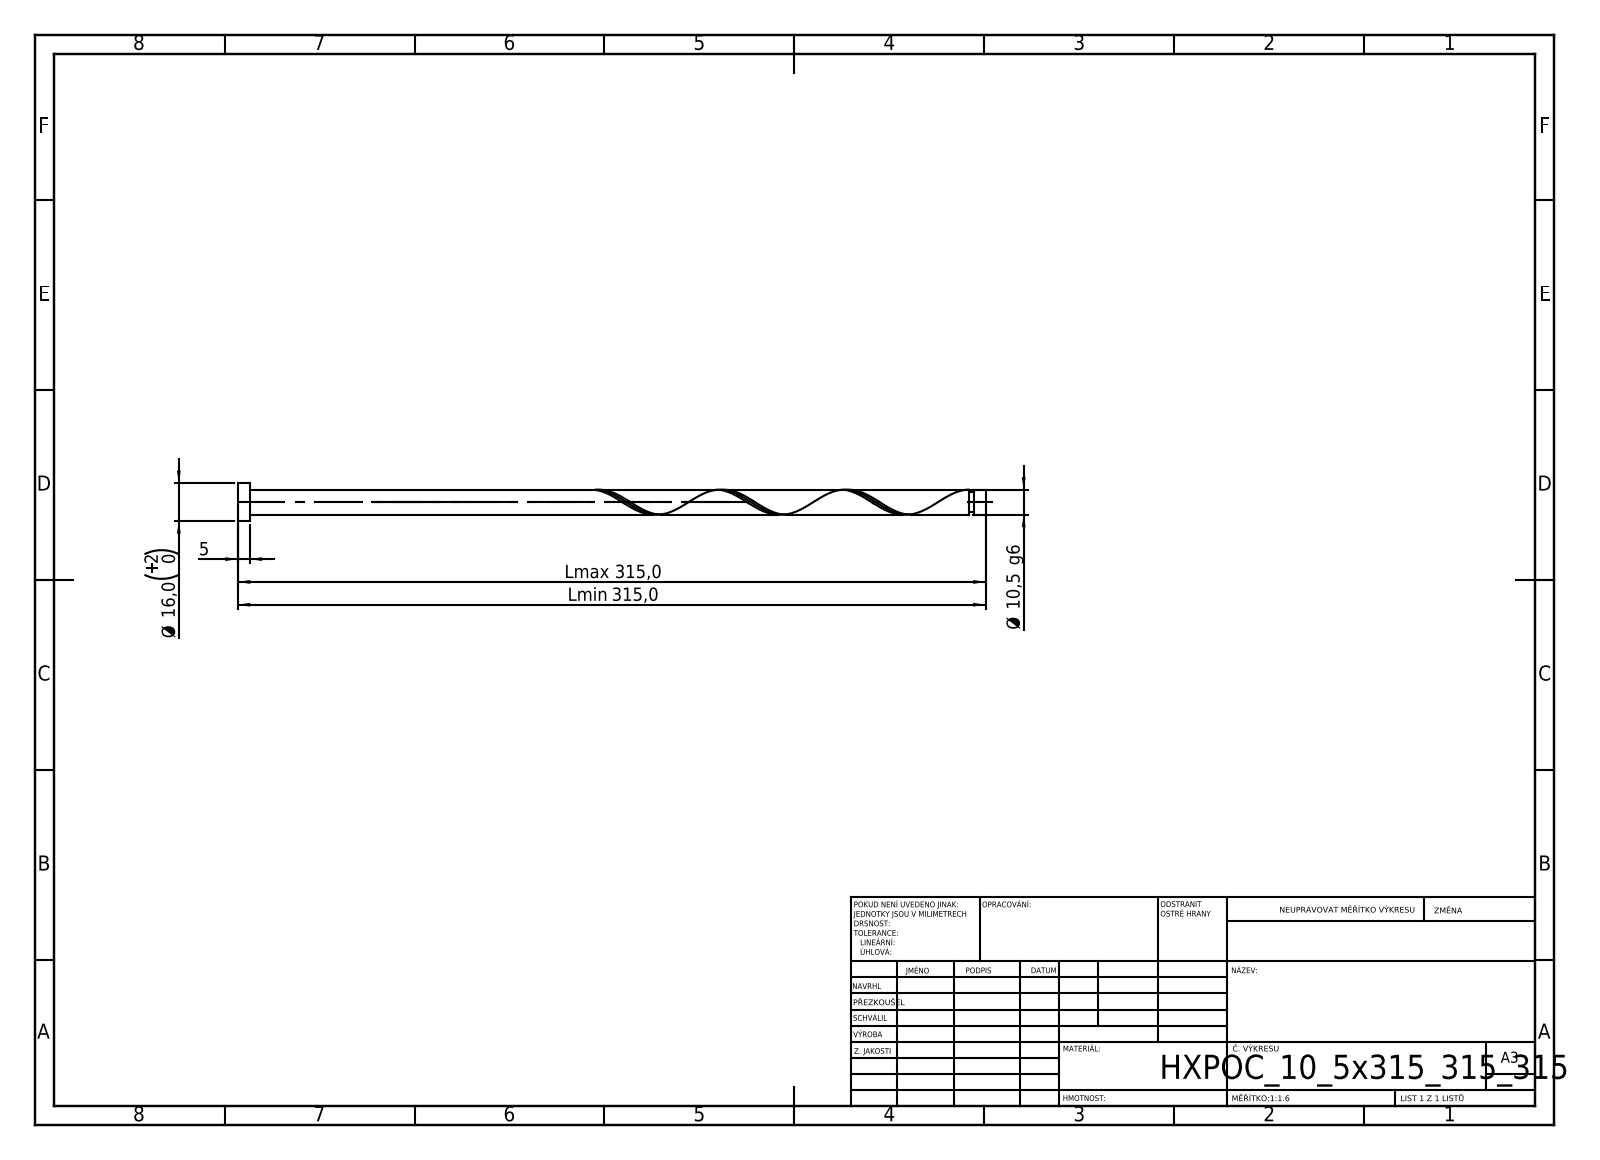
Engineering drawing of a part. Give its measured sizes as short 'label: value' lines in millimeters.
written by: SolidWorks 2019 (CONFIG_CONTROL_DESIGN)
unit: mm
bodies: 1 solid, 21 faces (6 planar, 14 cylindrical, 1 other)
size: 315 × 16 × 16
volume: 27 522 mm³; area: 11 125 mm²
bosses: 1× ⌀16, 1× ⌀10.5, 1× ⌀8.4
face distances: 5, 315, 310, 310.11, 305.11, 4.89, 308.01, 303.01, 2.1, 6.99
